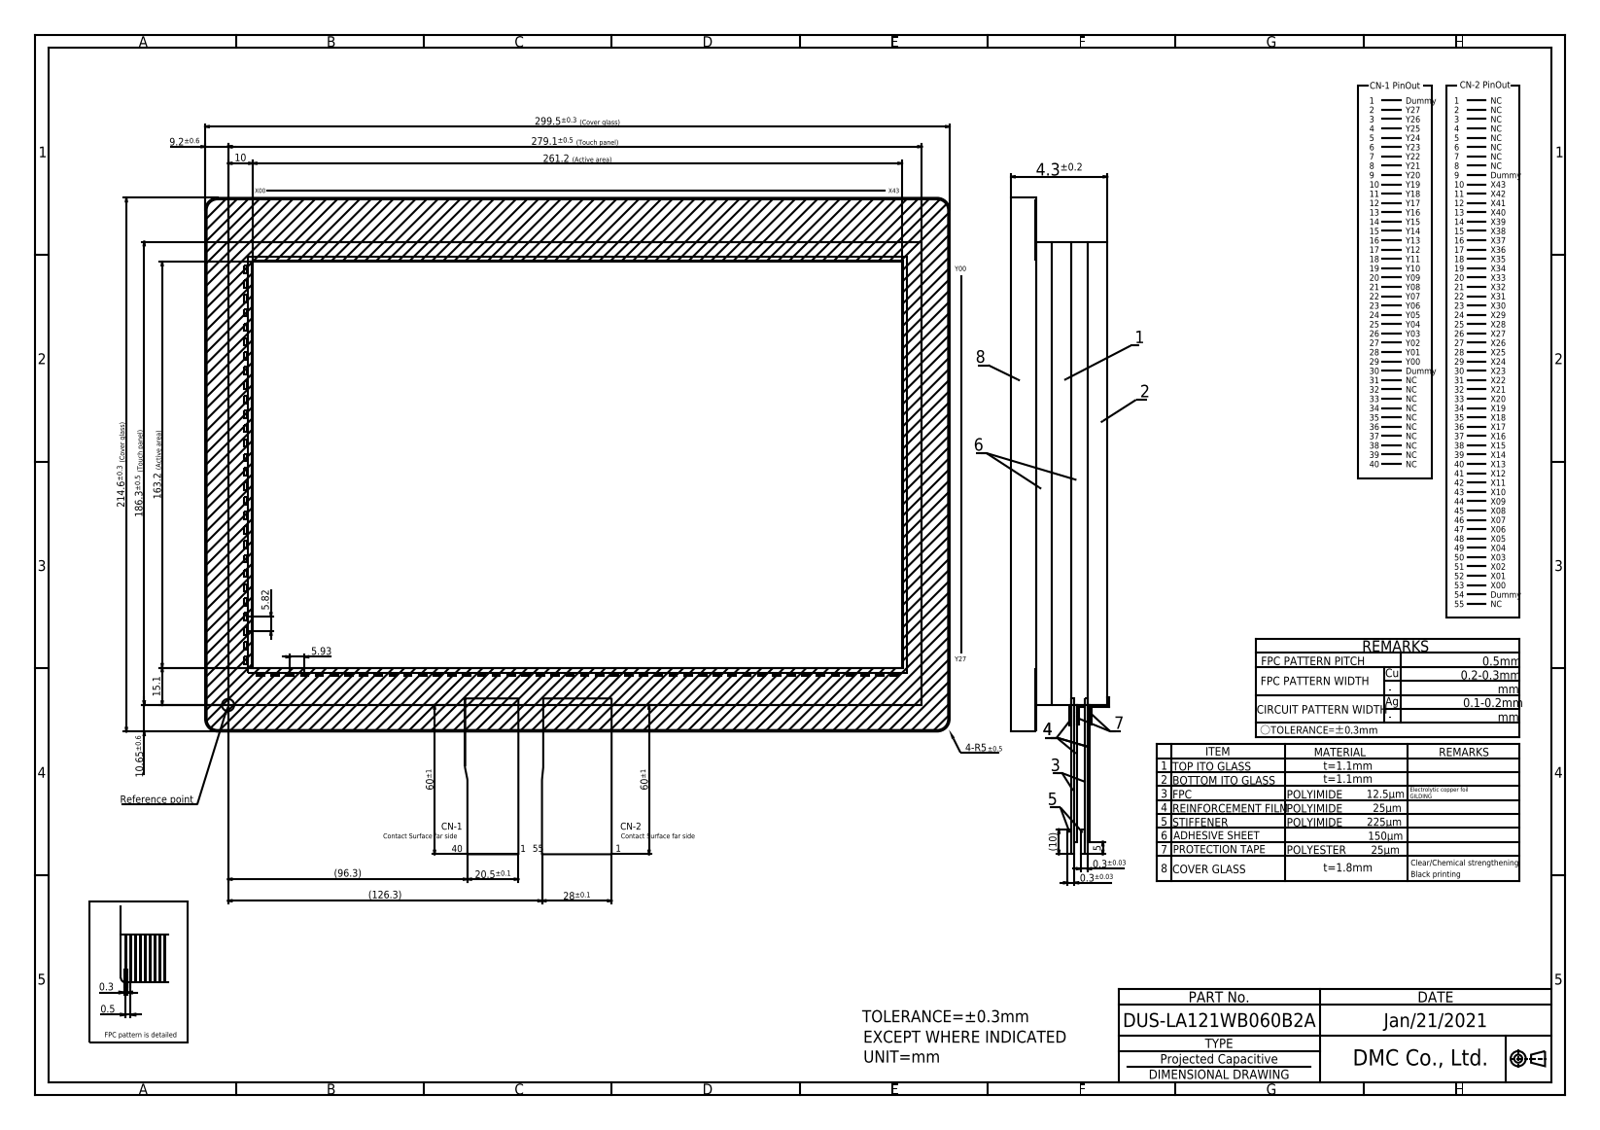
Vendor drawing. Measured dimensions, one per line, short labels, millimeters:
name: DUS-LA121WB060B2A
written by: Autodesk Inventor 2020 (CONFIG_CONTROL_DESIGN)
unit: mm
bodies: 1 solid, 425 faces (420 planar, 5 cylindrical, 0 other)
size: 419.3 × 306.87 × 4.3
volume: 241 793 mm³; area: 223 925 mm²
rounds: 4× R5, 1× R0.2
face distances: 1.8, 2.5, 4.3, 2.4, 1.9, 1.25, 1.15, 1.35, 3.15, 3.05
